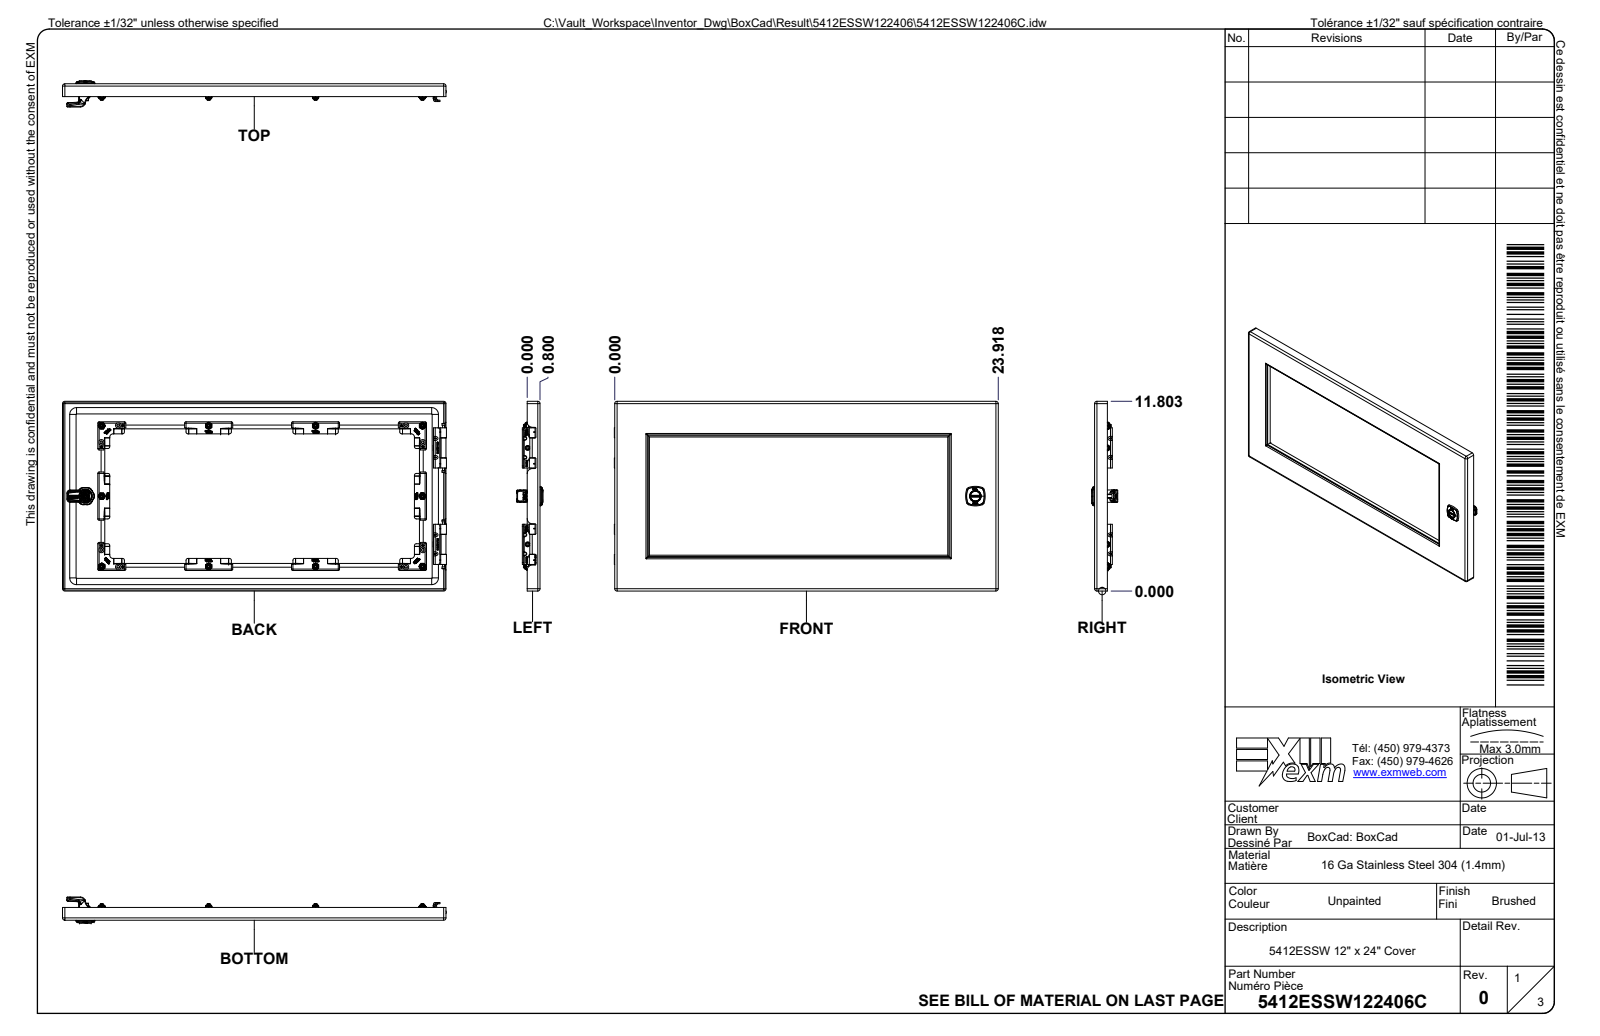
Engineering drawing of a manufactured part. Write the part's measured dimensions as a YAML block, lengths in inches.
part_name: "5412ESSW122406; 5412ESSW122406B; 5412ESSW122406B-P; STK-Q-16020 (+8 more)"
step_written_by: "Autodesk Inventor 2024 (AUTOMOTIVE_DESIGN)"
units: inches
bodies: {solids: 85, faces: 12270, planar: 5522, cylindrical: 2482, other: 4266}
overall_size: [24, 12, 7.306]
volume: 146.2
surface_area: 3386
round_holes:
  - {diameter: 0.29, count: 16}
  - {diameter: 0.03, count: 15}
  - {diameter: 0.315, count: 14}
  - {diameter: 0.201, count: 13}
  - {diameter: 0.197, count: 10}
  - {diameter: 0.276, count: 10}
  - {diameter: 0.374, count: 10}
  - {diameter: 0.173, count: 8}
  - {diameter: 0.044, count: 4}
  - {diameter: 0.27, count: 4}
  - {diameter: 0.39, count: 4}
  - {diameter: 0.236, count: 2}
round_bosses_or_shafts:
  - {diameter: 0.03, count: 15}
  - {diameter: 0.232, count: 14}
  - {diameter: 0.354, count: 10}
  - {diameter: 0.271, count: 8}
  - {diameter: 0.039, count: 8}
  - {diameter: 0.717, count: 4}
  - {diameter: 0.311, count: 4}
  - {diameter: 0.262, count: 4}
partial_cylinders:
  - {radius: 0.02, count: 156}
  - {radius: 0.031, count: 108}
  - {radius: 0.039, count: 90}
  - {radius: 0.086, count: 62}
  - {radius: 0.008, count: 54}
  - {radius: 0.035, count: 30}
  - {radius: 0.084, count: 28}
  - {radius: 0.008, count: 20}
face_to_face_distances: [0.053, 7.082, 11.947, 0.927, 0.874, 0.105, 1.032, 0.979, 6.51, 0.572]
hole_center_spacings: [1.028, 10.999, 1.026, 1.492, 1.591, 3.347, 4.374, 4.52]
